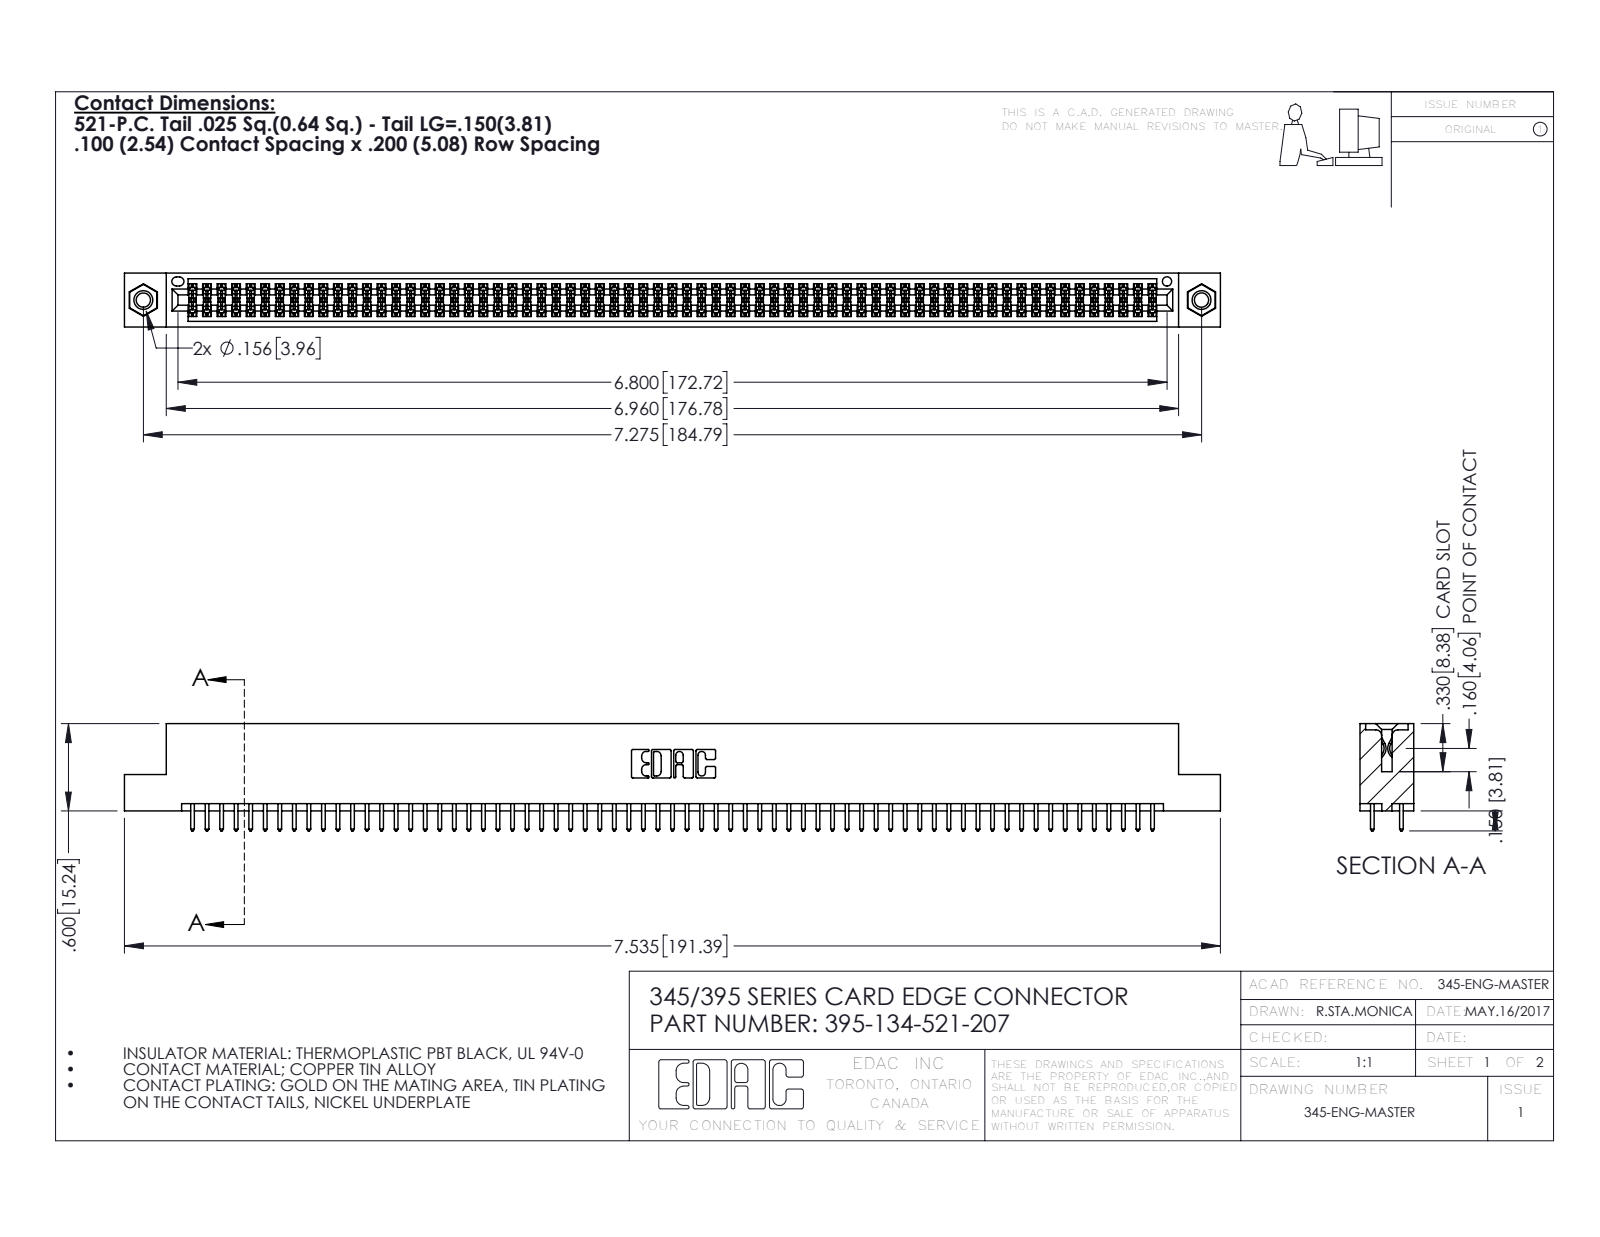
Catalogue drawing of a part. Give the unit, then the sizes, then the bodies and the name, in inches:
Units: inches
Overall size (bounding box): 7.535 × 0.737 × 0.37
Round holes (diameter × count): ⌀0.098 ×2, ⌀0.125 ×2, ⌀0.156 ×2, ⌀0.064 ×1
Round bosses / shafts (diameter × count): ⌀0.155 ×2
Partial cylindrical surfaces — rounded edges, fillets, slot ends (radius × count): R0.006 ×201, R0.01 ×134, R0.01 ×22, R0.007 ×6, R0.031 ×6, R0.026 ×3, R0.014 ×2, R0.019 ×2
Main face-to-face distances: 0.072, 0.298, 0.2, 0.098, 0.272, 0.025, 0.37, 0.225, 0.175, 0.149
Hole centre spacings: 0.27, 7.039, 7.275
Volume: 1.145 in³ · Surface area: 43.21 in²
Bodies: 137 solids, 6886 faces (4534 planar, 2336 cylindrical, 16 other)
Part name (STEP PRODUCT): 345-250-001_345-250-005-103; 395-134-521-207; 345-292-001_345-293-121; 345 Part_Flush Mounting Lugs - 0.156 Dia-TI
STEP written by: SolidWorks 2016 (CONFIG_CONTROL_DESIGN)
